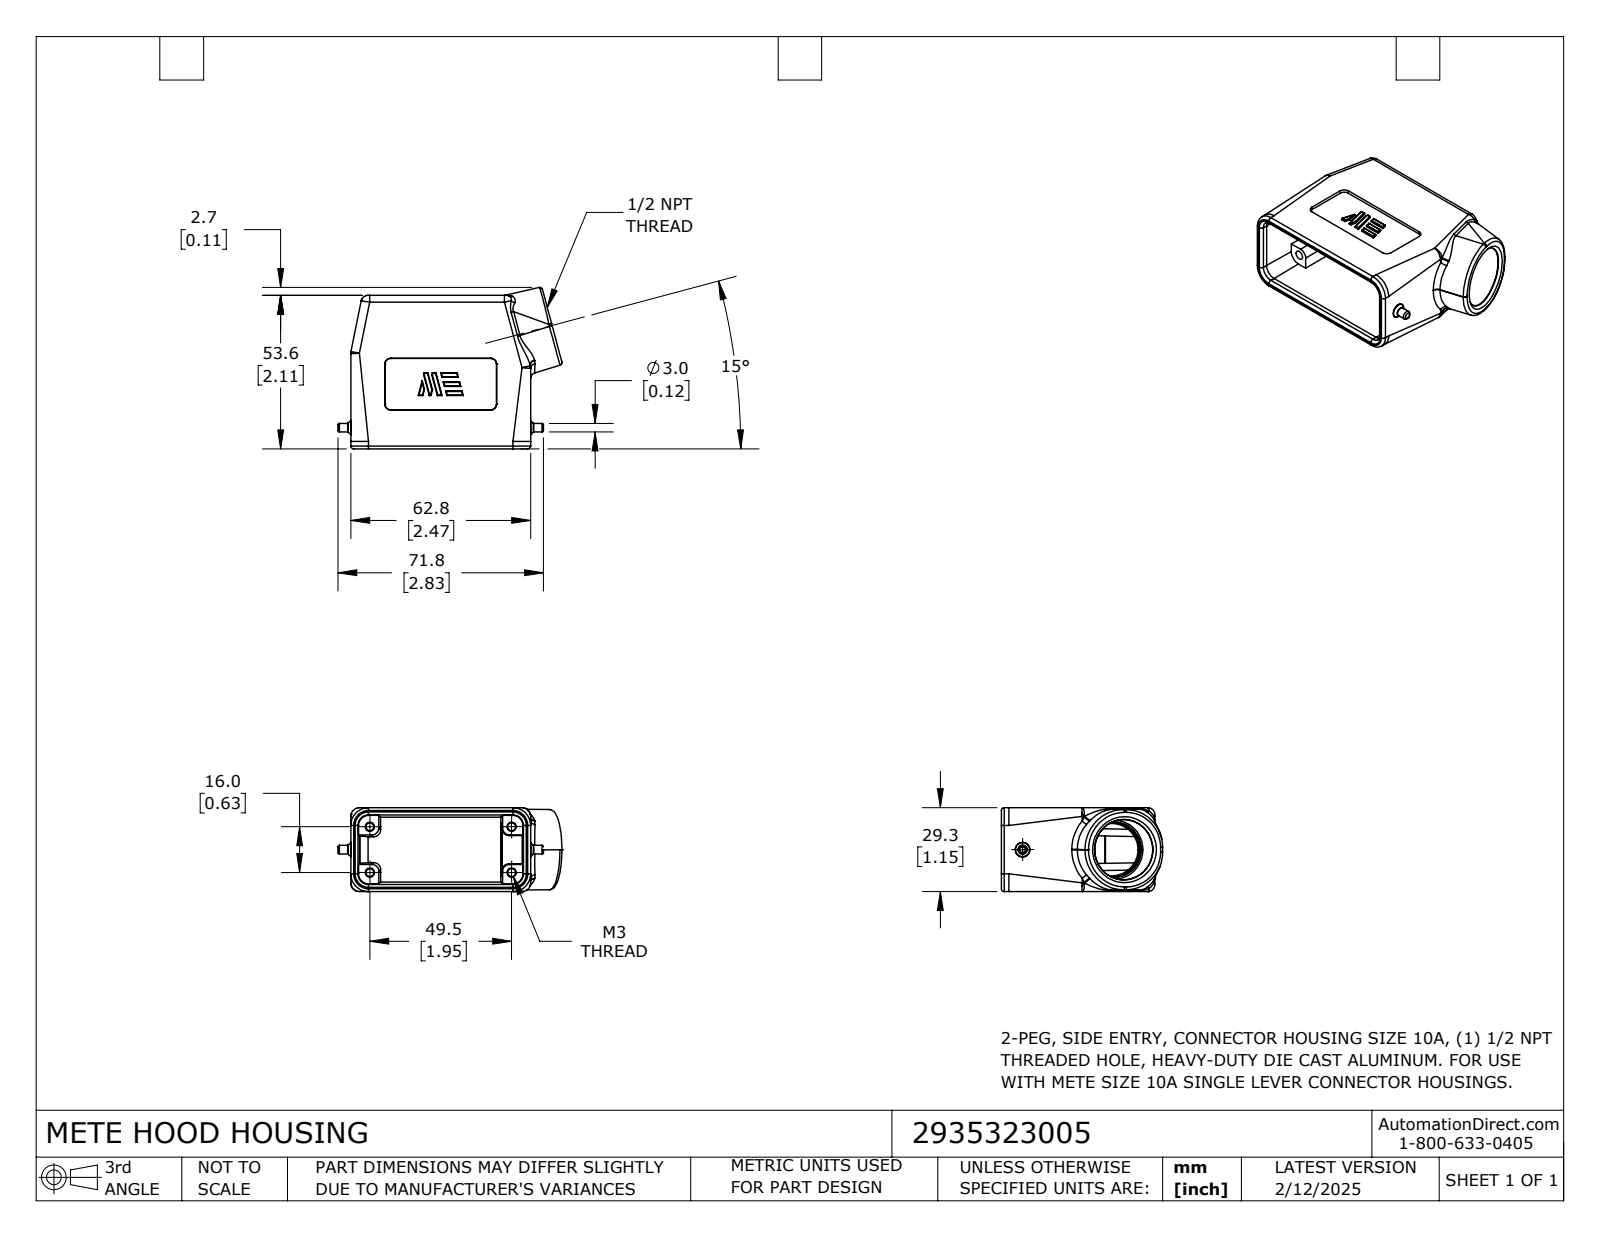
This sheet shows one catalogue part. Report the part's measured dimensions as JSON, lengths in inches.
{"part_name": "2935323005", "step_written_by": "SolidWorks 2024 (CONFIG_CONTROL_DESIGN)", "units": "inches", "bodies": {"solids": 1, "faces": 316, "planar": 119, "cylindrical": 101, "other": 96}, "overall_size": [3.08, 2.219, 1.154], "volume_in3": 2.09, "surface_area_in2": 34.38, "round_bosses_or_shafts": [[0.118, 1]], "partial_cylinders_radius": [[0.008, 38], [0.039, 13], [0.079, 4], [0.094, 4], [0.098, 4], [0.118, 4], [0.146, 4], [0.244, 4]], "face_to_face_distances": [1.154, 0.098, 1.114, 0.039, 1.075, 0.279, 2.472, 0.267, 0.02, 1.055]}
